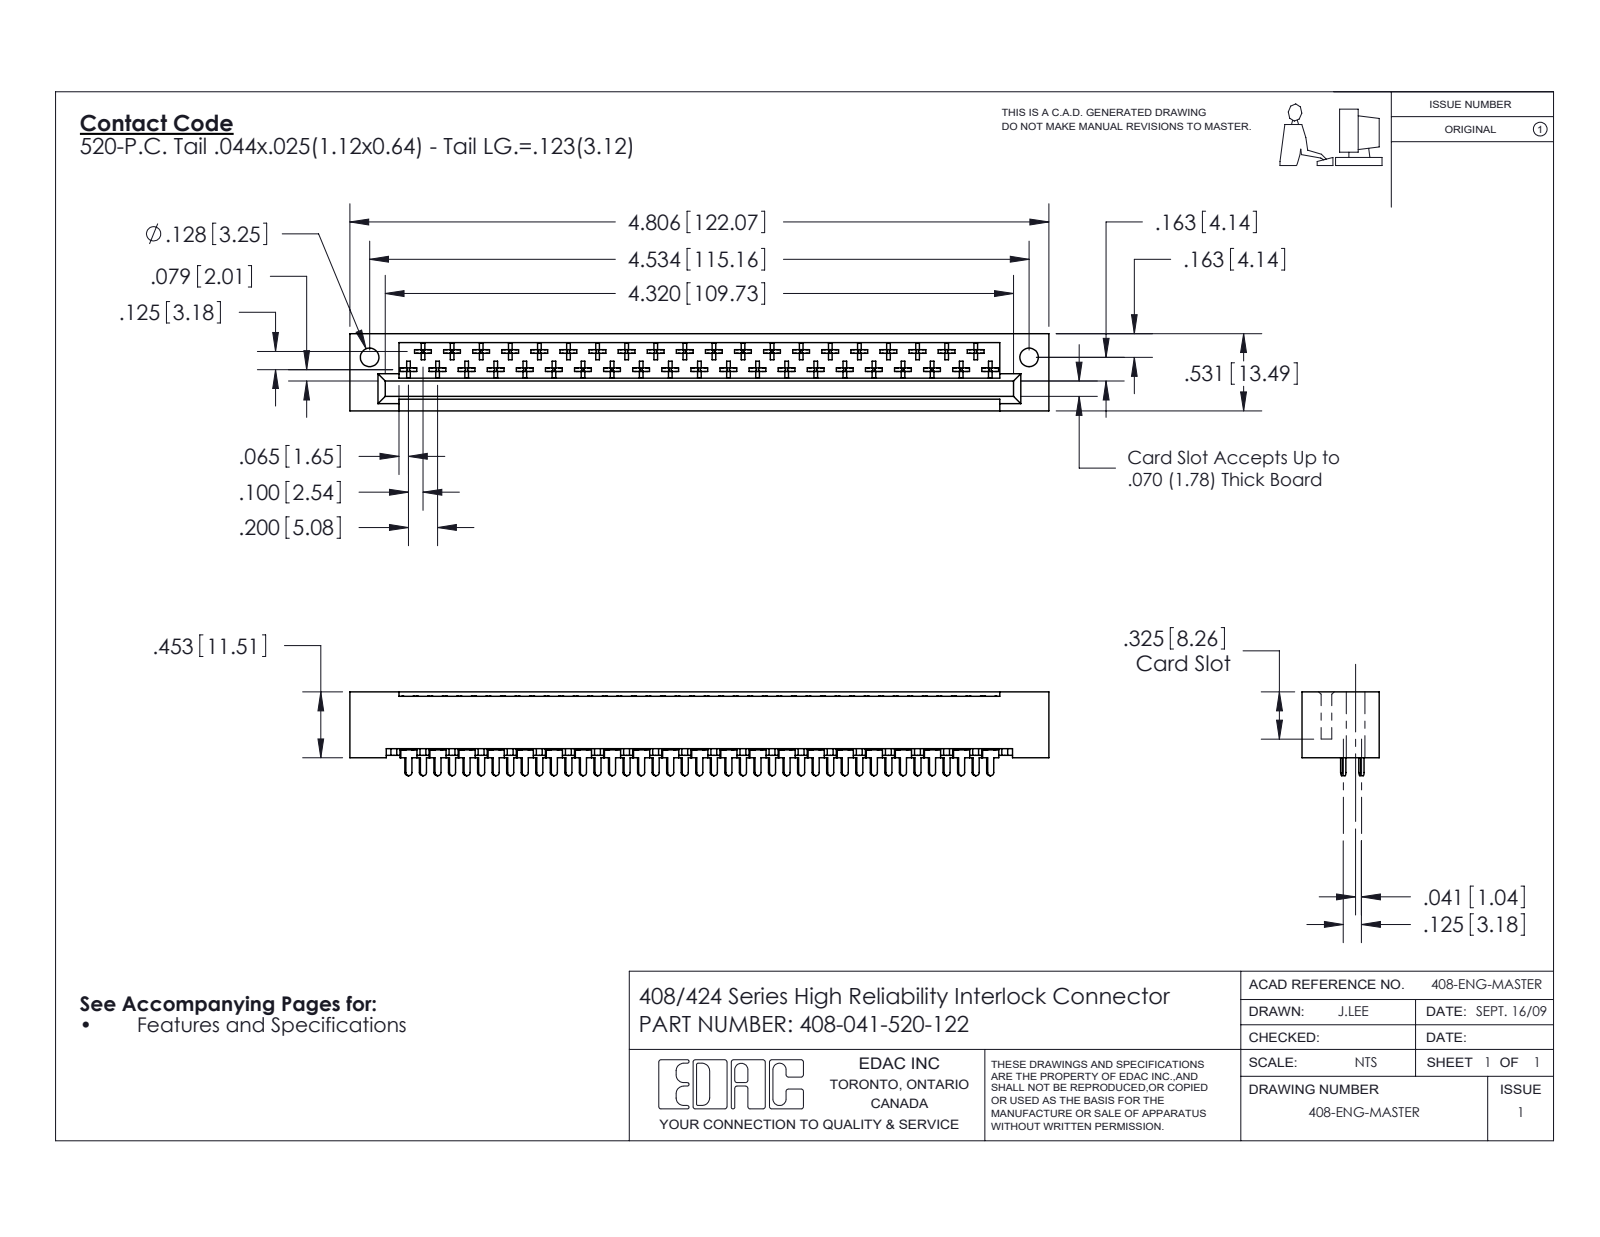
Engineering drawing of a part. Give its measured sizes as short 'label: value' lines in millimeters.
name: 408-041-520-122; 408-290-001_408-290-120; 408 Part_041 - 1
written by: SolidWorks 2016 (CONFIG_CONTROL_DESIGN)
unit: mm
bodies: 42 solids, 2299 faces (1758 planar, 377 cylindrical, 164 other)
size: 122.1 × 14.6 × 13.5
volume: 13 300 mm³; area: 16 590 mm²
holes: 2× ⌀3.3
rounds: 246× R0.3, 43× R0.5, 41× R0.6
face distances: 2.5, 7.5, 13.5, 3.2, 0.6, 0.6, 6.6, 6.9, 6, 3.4
hole spacings: 115.2
